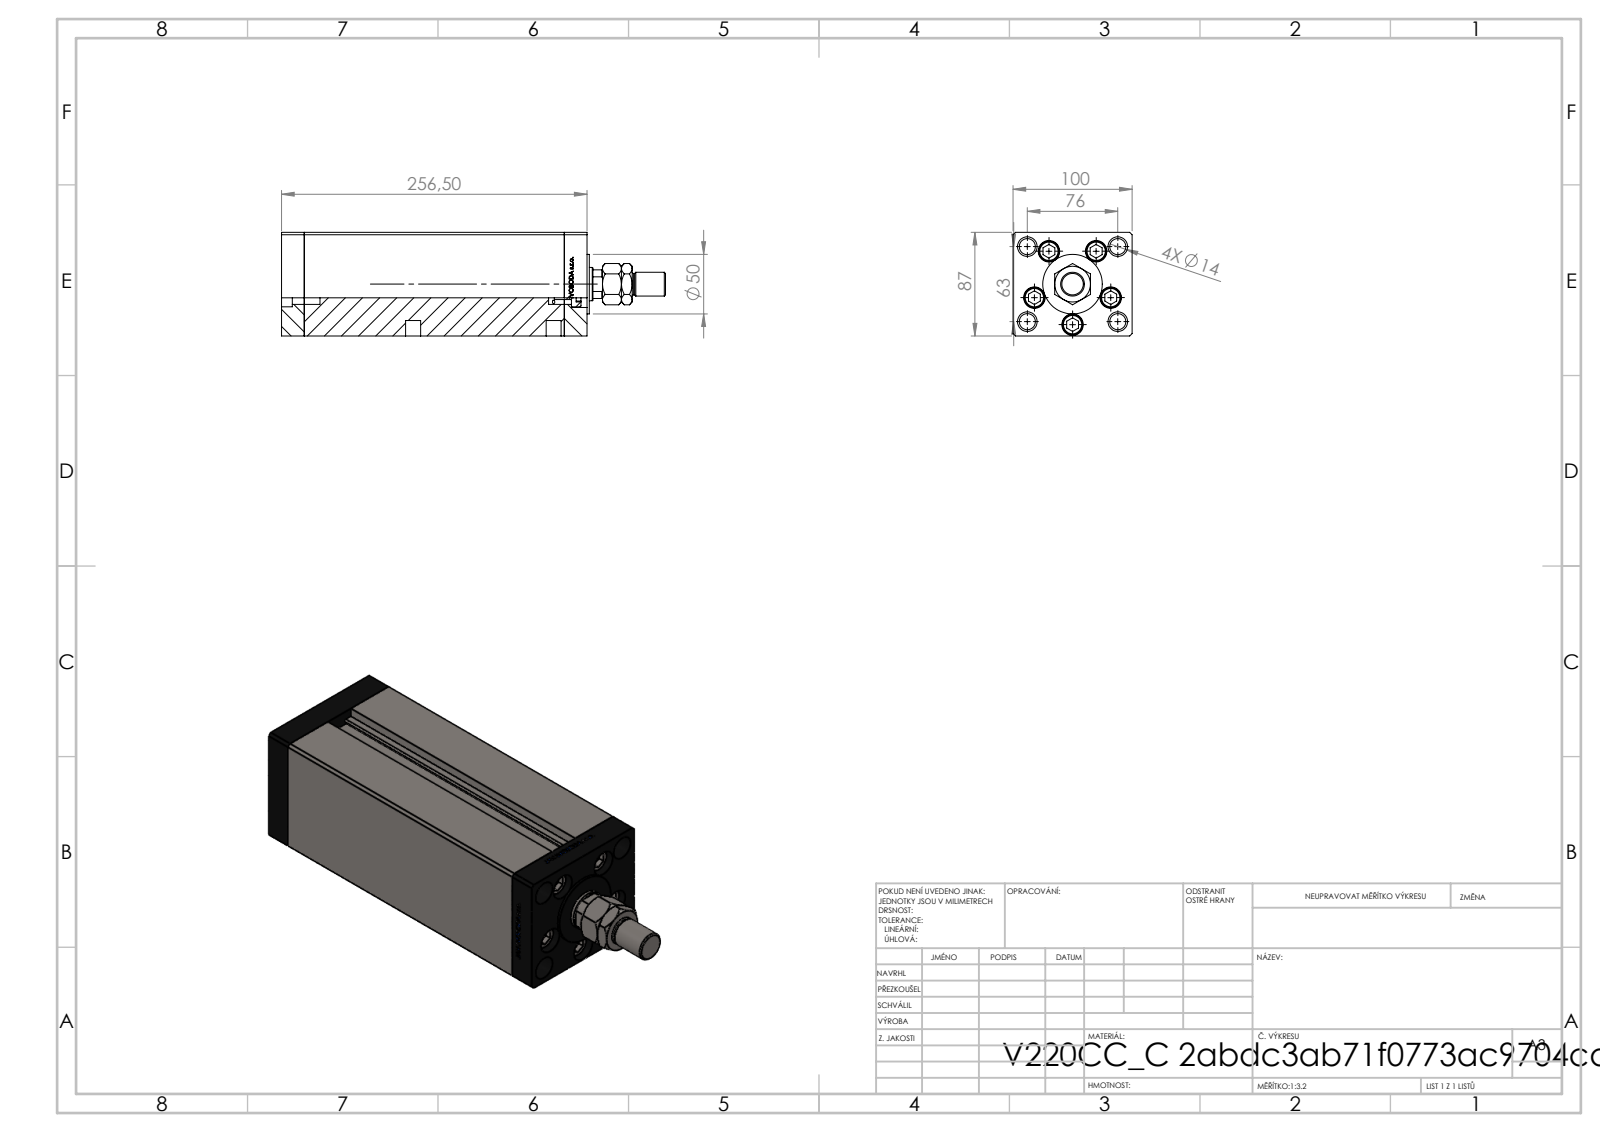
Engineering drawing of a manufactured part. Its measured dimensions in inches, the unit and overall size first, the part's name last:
Units: inches
Overall size (bounding box): 12.697 × 3.937 × 3.425
Round holes (diameter × count): ⌀0.531 ×9, ⌀0.709 ×5, ⌀0.079 ×4, ⌀0.472 ×4, ⌀0.518 ×4, ⌀0.65 ×4, ⌀0.669 ×1, ⌀0.728 ×1, ⌀1.102 ×1
Round bosses / shafts (diameter × count): ⌀0.315 ×5, ⌀0.669 ×4, ⌀1.969 ×1, ⌀0.787 ×1, ⌀0.709 ×1
Partial cylindrical surfaces — rounded edges, fillets, slot ends (radius × count): R0.037 ×2, R0.531 ×1
Main face-to-face distances: 3.937, 3.425, 0.748, 8.602, 9.35, 1.348, 10.098, 8.75, 8.002, 0.6
Hole centre spacings: 1.339, 1.943, 0.732, 0.828, 1.499, 1.546, 1.607, 1.702
Volume: 112.8 in³ · Surface area: 442.3 in²
Bodies: 14 solids, 1235 faces (563 planar, 180 cylindrical, 492 other)
Part name (STEP PRODUCT): V220C_VC_C; V220C BACK_C; ALLEN BOLT; MTA (+2 more)
STEP written by: SolidWorks 2019 (CONFIG_CONTROL_DESIGN)
